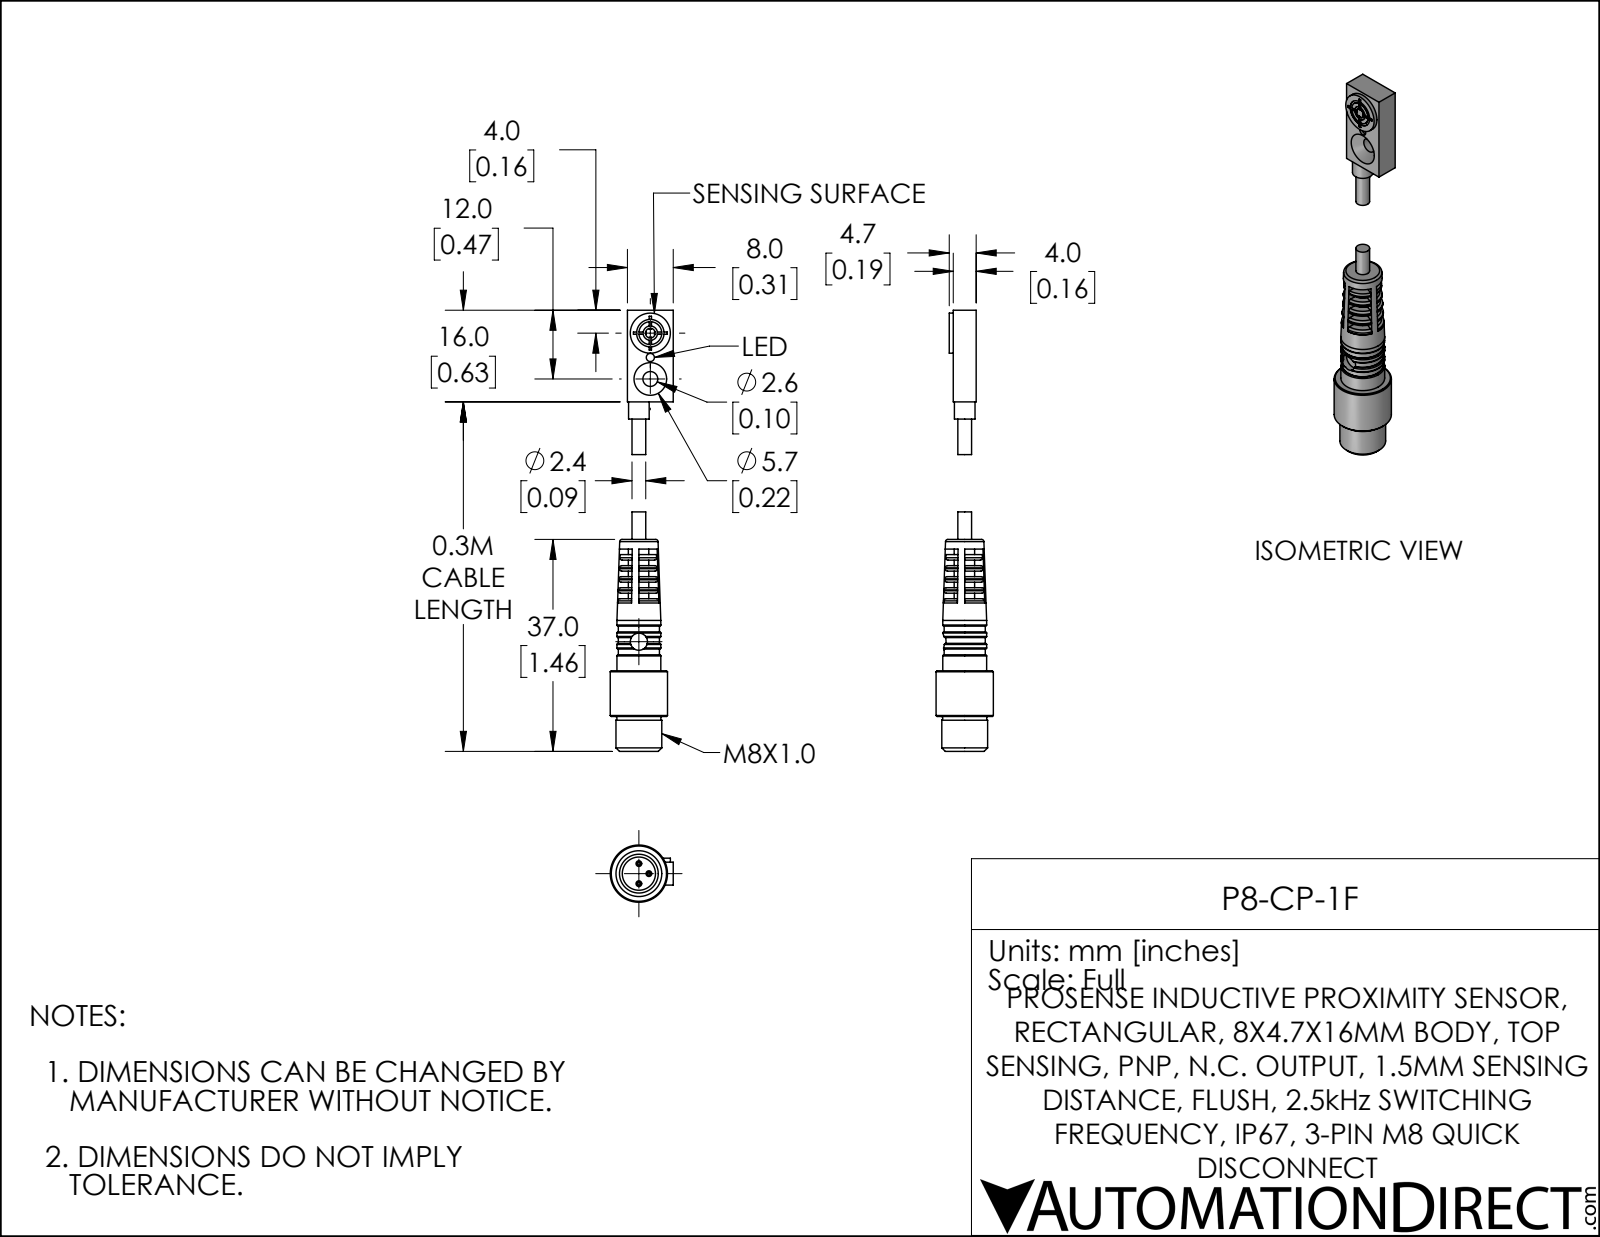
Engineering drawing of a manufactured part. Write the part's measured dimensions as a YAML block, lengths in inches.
part_name: "P8-CP-1F_2; P8-CP-1F; P8-CP-1F_1"
step_written_by: "SolidWorks 2019 (AUTOMOTIVE_DESIGN)"
units: inches
bodies: {solids: 2, faces: 240, planar: 116, cylindrical: 56, other: 68}
overall_size: [2.896, 0.433, 0.394]
volume: 0.135
surface_area: 3.16
round_holes:
  - {diameter: 0.056, count: 1}
  - {diameter: 0.098, count: 1}
  - {diameter: 0.102, count: 1}
  - {diameter: 0.118, count: 1}
  - {diameter: 0.189, count: 1}
  - {diameter: 0.228, count: 1}
round_bosses_or_shafts:
  - {diameter: 0.039, count: 3}
  - {diameter: 0.394, count: 1}
  - {diameter: 0.315, count: 1}
  - {diameter: 0.302, count: 1}
  - {diameter: 0.283, count: 1}
  - {diameter: 0.276, count: 1}
  - {diameter: 0.157, count: 1}
  - {diameter: 0.142, count: 1}
partial_cylinders:
  - {radius: 0.033, count: 1}
  - {radius: 0.072, count: 1}
face_to_face_distances: [0.038, 0.152, 0.114, 0.315, 0.157, 0.076, 0.076, 0.189, 0.303, 0.265]
hole_center_spacings: [0.148, 0.167, 0.315]
